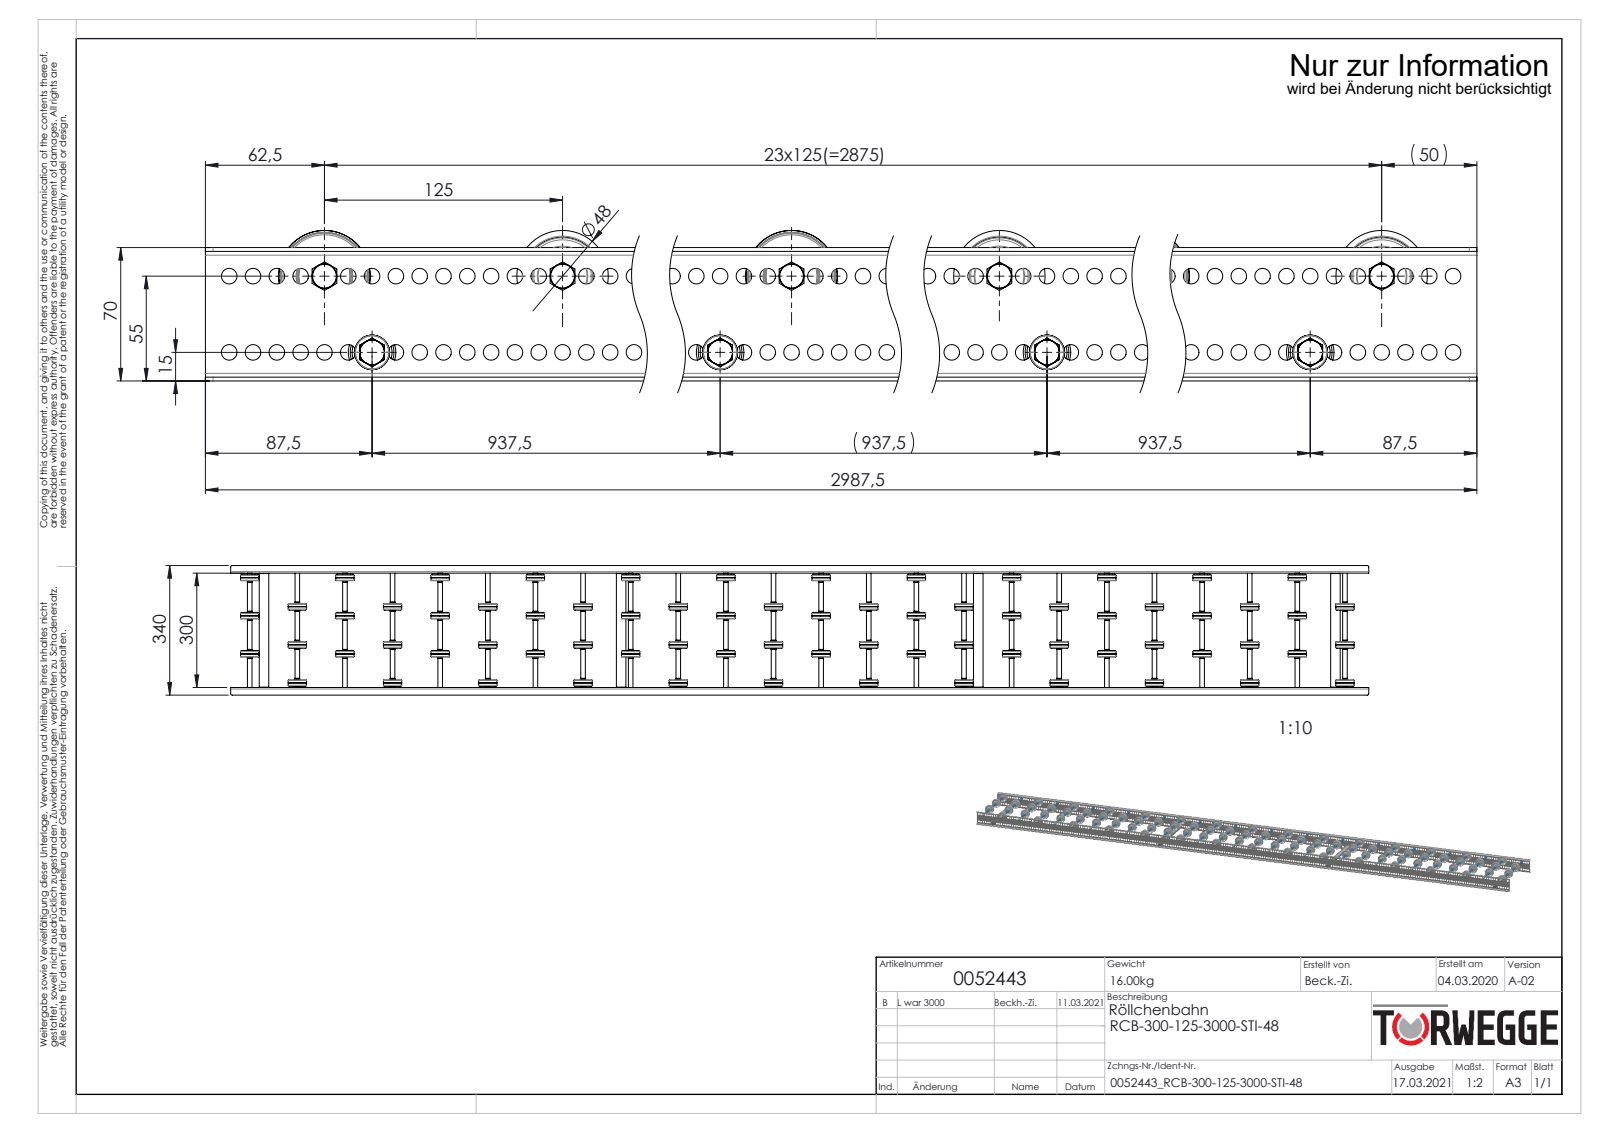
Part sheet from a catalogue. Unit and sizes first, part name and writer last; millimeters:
Units: millimetres
Overall size (bounding box): 2987.5 × 340 × 79
Round holes (diameter × count): ⌀8.2 ×476, ⌀6.65 ×24, ⌀8 ×24, ⌀9.65 ×24, ⌀15 ×24, ⌀41 ×24, ⌀6.8 ×4, ⌀21 ×4
Round bosses / shafts (diameter × count): ⌀48 ×24, ⌀13 ×24, ⌀12.5 ×24, ⌀12.4 ×24, ⌀12 ×24, ⌀11.5 ×24, ⌀25 ×4, ⌀8 ×4
Partial cylindrical surfaces — rounded edges, fillets, slot ends (radius × count): R4 ×8, R2 ×4
Main face-to-face distances: 2, 302, 68, 100, 304, 300, 76, 70, 66, 12
Hole centre spacings: 12.5, 25, 37.5, 50, 62.5, 75, 87.5, 100
Volume: 3 532 000 mm³ · Surface area: 2 907 000 mm²
Bodies: 310 solids, 10140 faces (1932 planar, 4400 cylindrical, 3808 other)
Part name (STEP PRODUCT): Profil_LRB-20x70x20x2_KFG_S109080_U-PROFIL-20-70-20-2-LRB-L=2987,5; S106837_Gewindestange-M8-KFG_L320; Traversen_KFG_L300; Hutmutter_DIN_1587_M8 (+5 more)
STEP written by: SolidWorks 2020 (AUTOMOTIVE_DESIGN)
